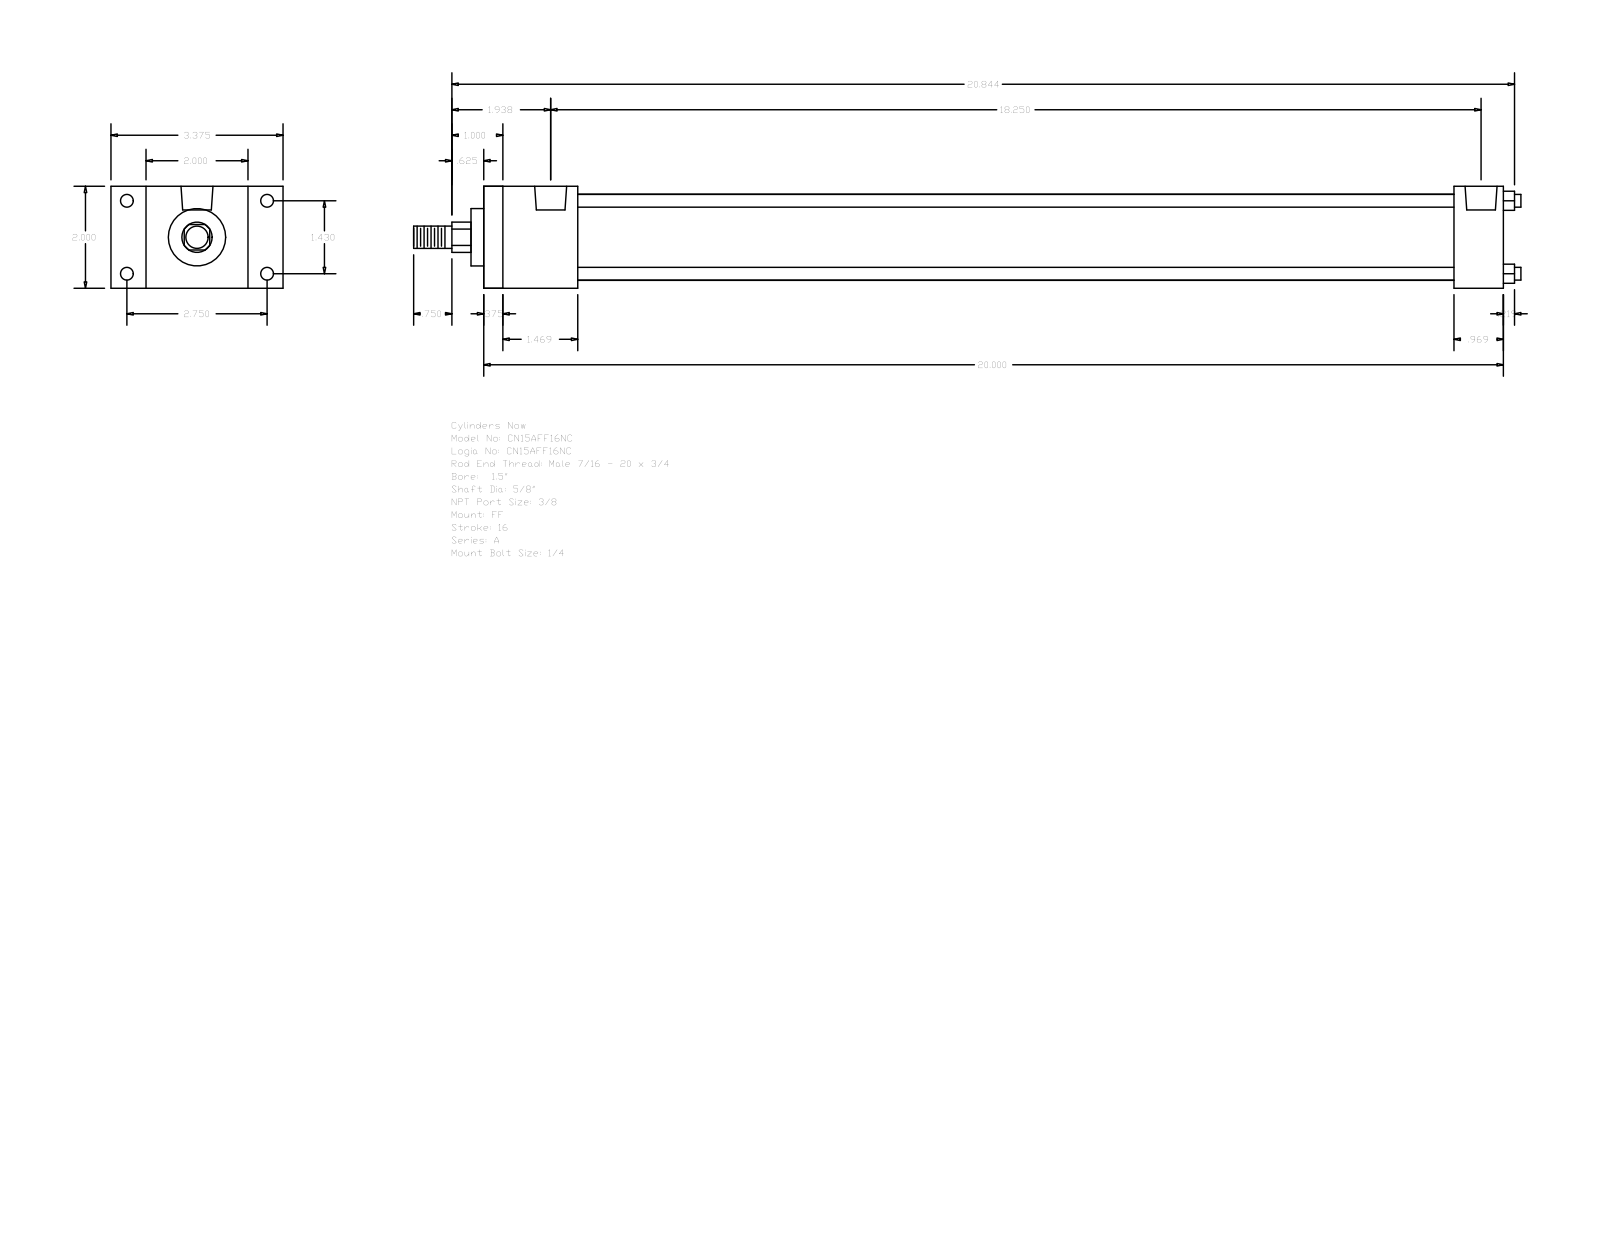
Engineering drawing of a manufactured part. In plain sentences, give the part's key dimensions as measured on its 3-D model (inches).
The part is named "A_FF__0150_0.625". Its 3-D file was written by "GSSL Pune (CONFIG_CONTROL_DESIGN)". It is 0 solids with 92 faces: 64 planar, 28 cylindrical and 0 other. Overall it measures 21.719 by 3.375 by 2 inches. Round holes: 4 of diameter 0.219, 4 of diameter 0.25, 2 of diameter 0.627. Round bosses or shafts: 4 of diameter 0.25, 1 of diameter 1.69, 1 of diameter 1.125, 1 of diameter 0.625, 1 of diameter 0.437. Partial cylindrical surfaces (rounded edges, fillets, slot ends): 1 of radius 0.297. The main face-to-face distances are 2, 20, 0.375, 19.625, 1.844, 19.031, 1.469, 18.656, 17.187, 18.156. The hole center spacings are 0.156, 1.43, 2.75, 3.099, 17.937, 18.094, 18.25.
